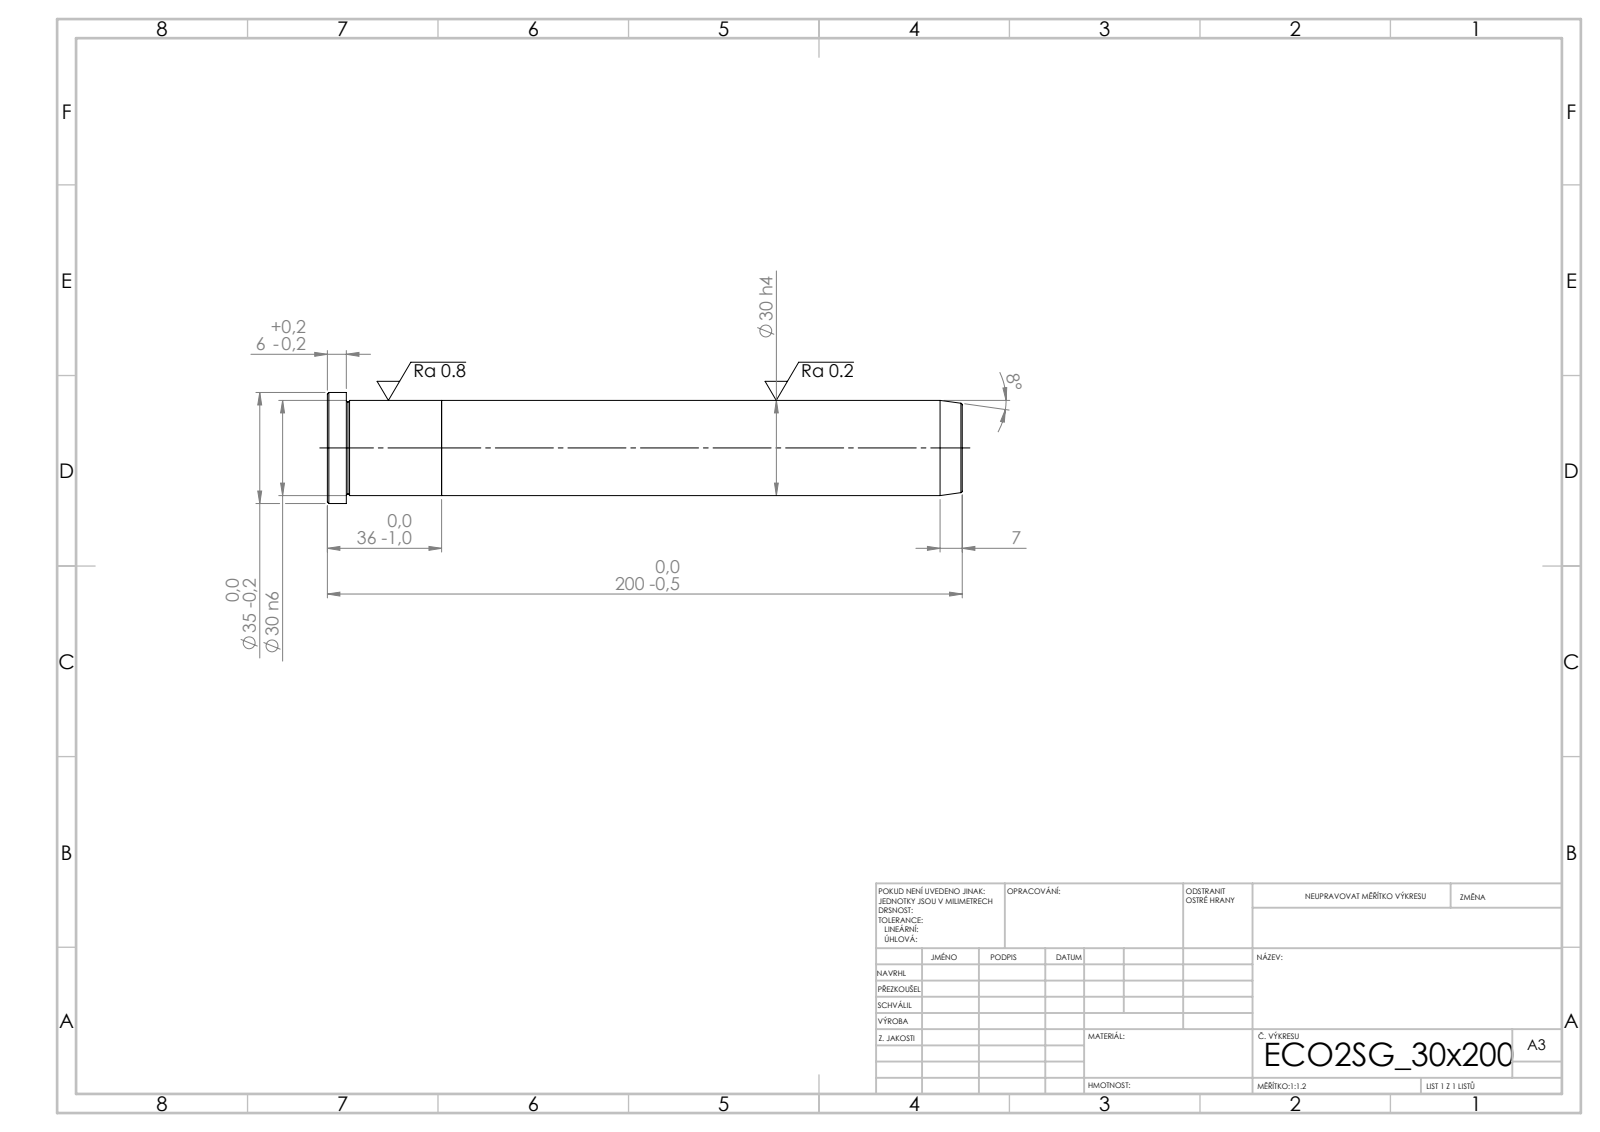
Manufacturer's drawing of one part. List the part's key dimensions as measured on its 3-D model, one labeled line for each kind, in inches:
STEP written by: SolidWorks 2019 (CONFIG_CONTROL_DESIGN)
Units: inches
Bodies: 2 solids, 21 faces (5 planar, 6 cylindrical, 10 other)
Overall size (bounding box): 7.874 × 1.378 × 1.378
Volume: 8.698 in³ · Surface area: 34.38 in²
Round bosses / shafts (diameter × count): ⌀1.378 ×1, ⌀1.181 ×1
Main face-to-face distances: 1.417, 6.457, 7.874, 7.638, 1.181, 0.236
